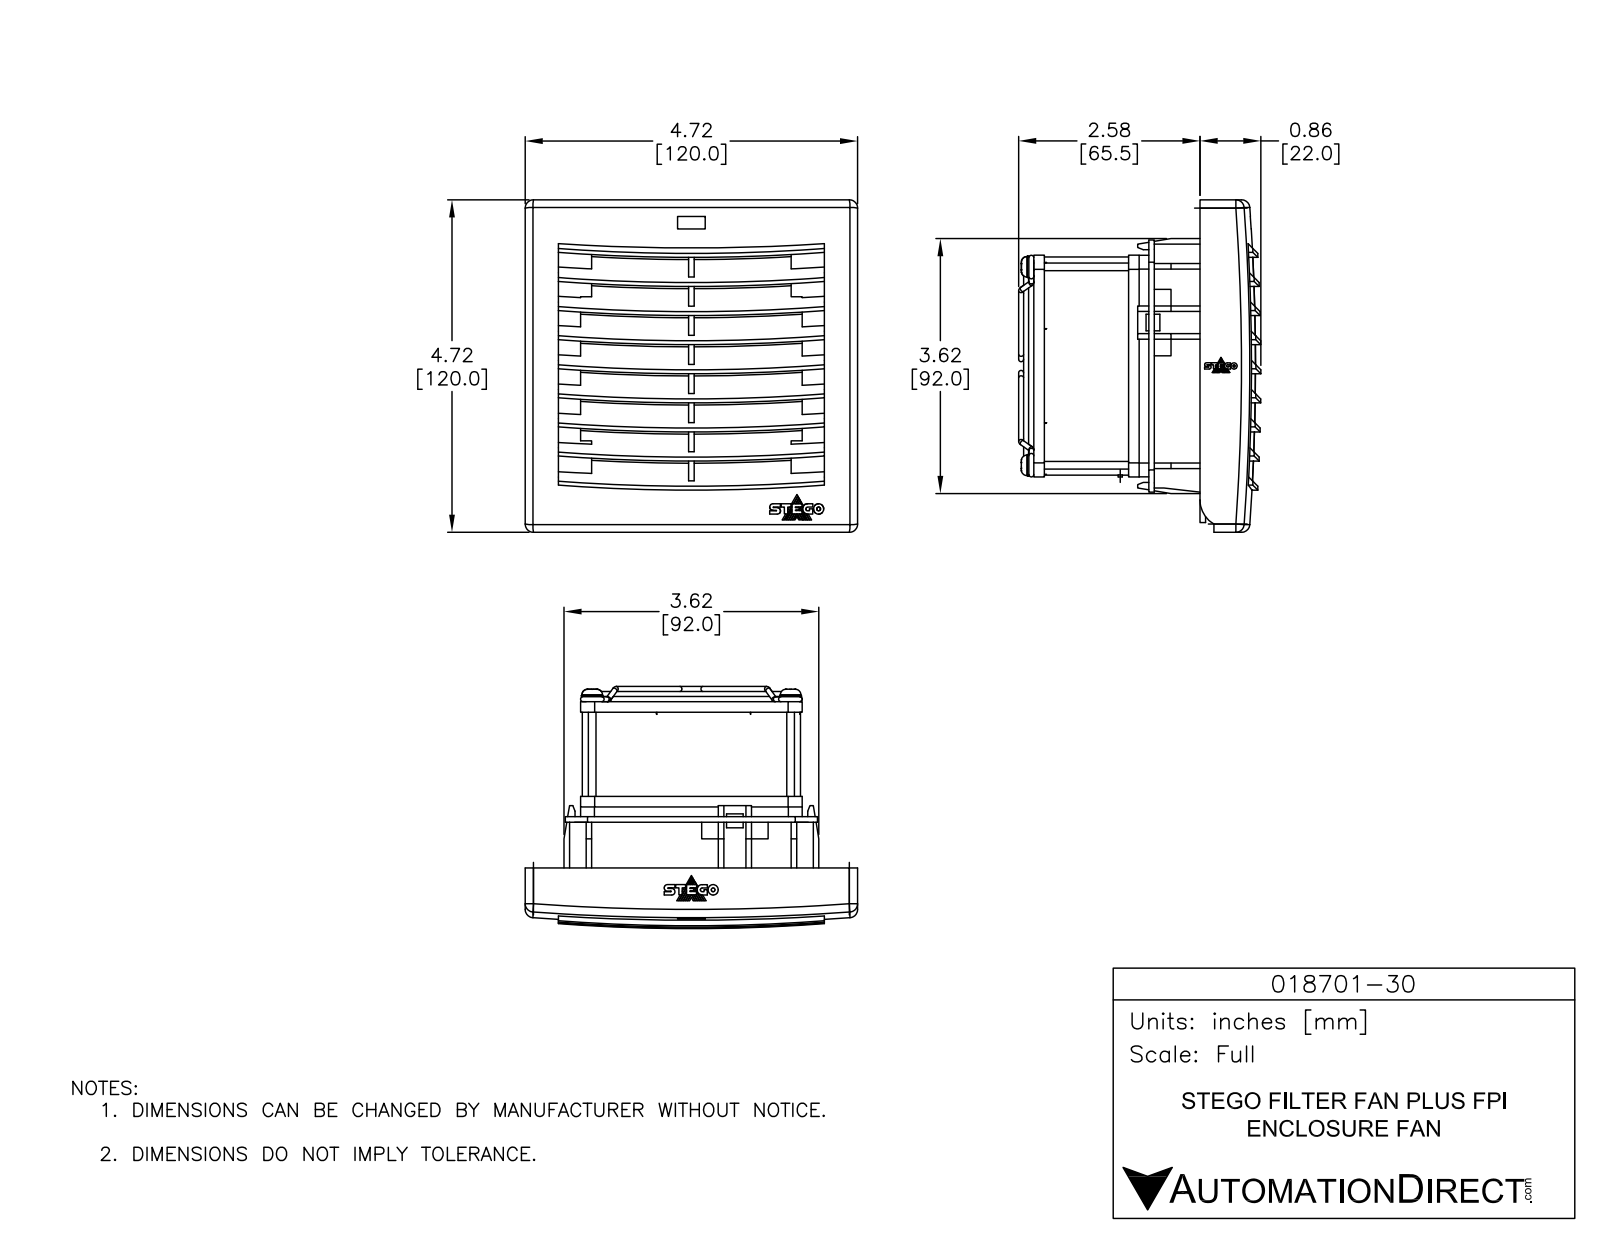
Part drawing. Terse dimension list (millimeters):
name: 018700-30
written by: SolidWorks 2018 (AUTOMOTIVE_DESIGN)
unit: mm
bodies: 15 solids, 607 faces (303 planar, 171 cylindrical, 133 other)
size: 120 × 120 × 87.5
volume: 276 800 mm³; area: 136 600 mm²
holes: 3× ⌀4.4, 2× ⌀4.4, 1× ⌀75.6, 1× ⌀78.7
bosses: 12× ⌀1.8, 4× ⌀7.8, 4× ⌀2.9, 1× ⌀46.9
rounds: 40× R0.6, 20× R0.2, 7× R0.2, 7× R31.4, 7× R31.4, 4× R1.4, 4× R1.7, 4× R3.2
face distances: 7.4, 2, 14.9, 22.3, 29.7, 102, 18, 3.6, 3.8, 11.2
hole spacings: 71.6, 50.6, 101.3, 50.6, 50.6
